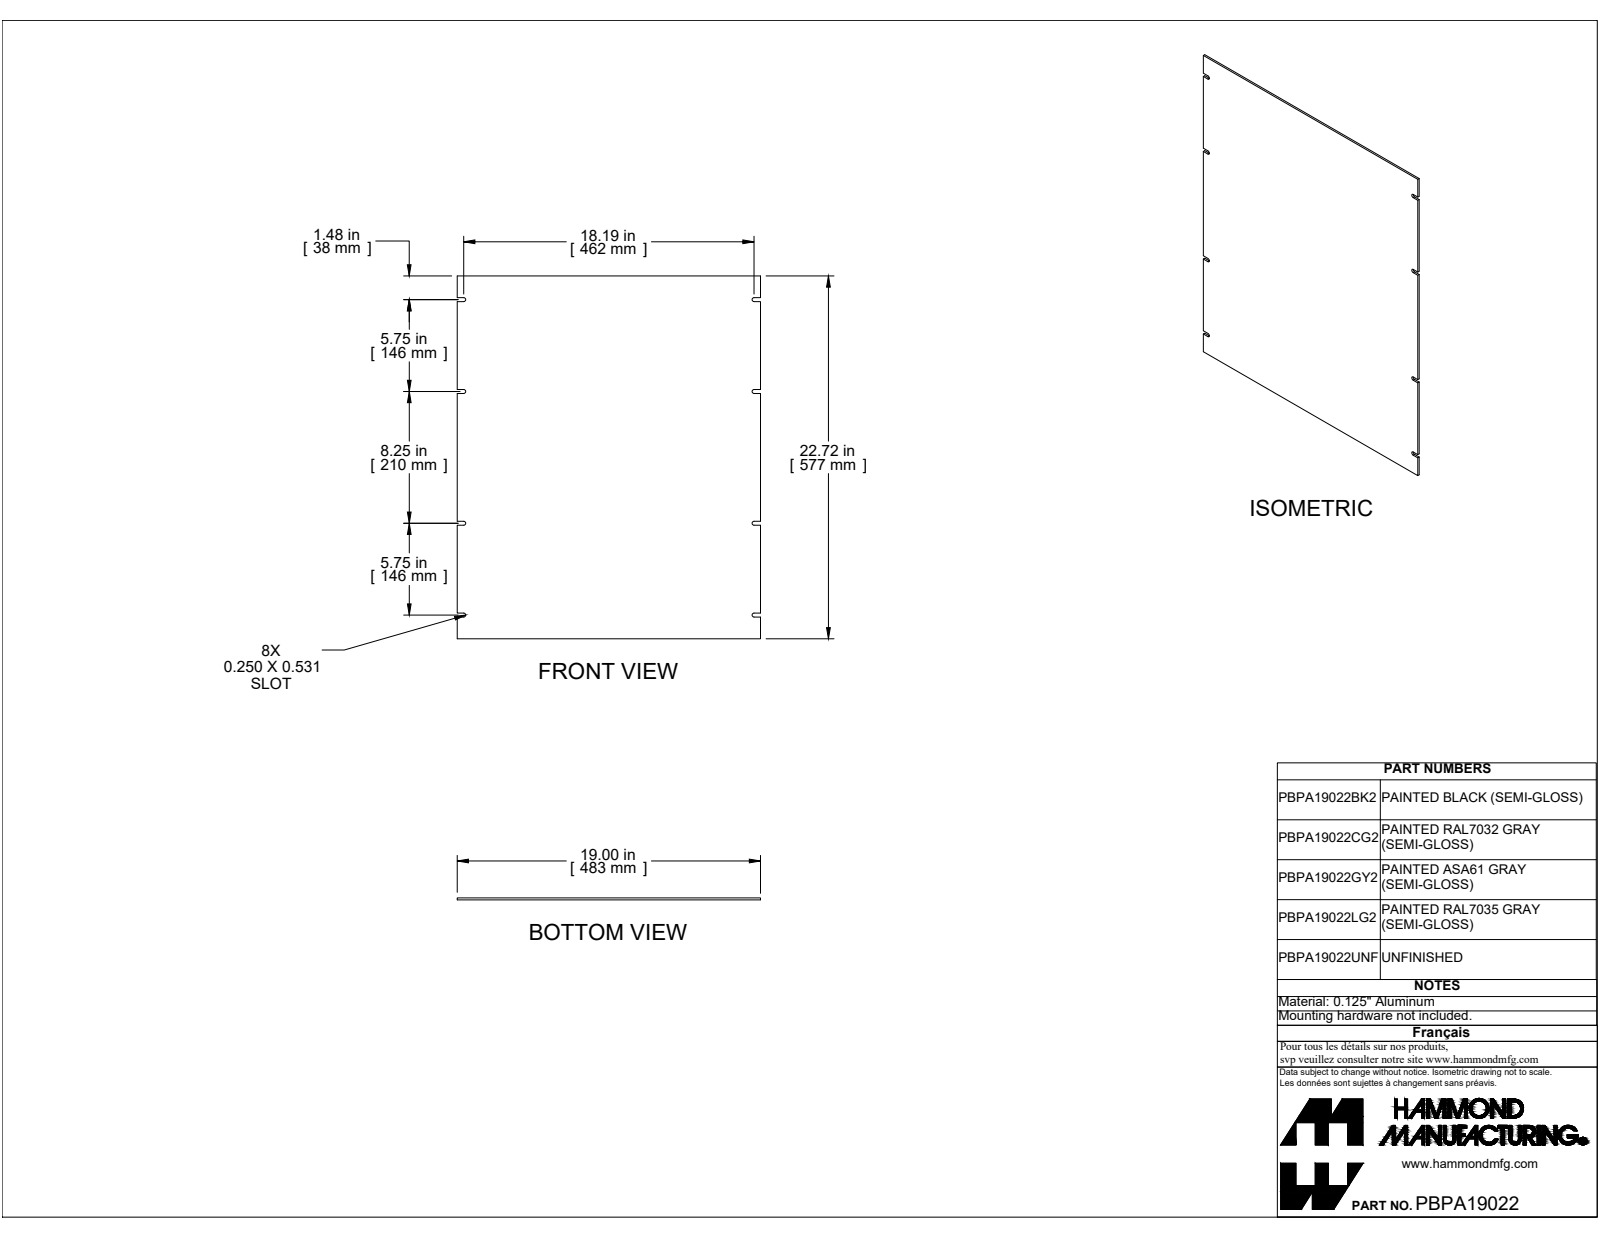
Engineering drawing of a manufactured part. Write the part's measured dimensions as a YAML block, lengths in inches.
part_name: "PBPA19022GY2"
step_written_by: "SolidWorks 2019 (CONFIG_CONTROL_DESIGN)"
units: inches
bodies: {solids: 1, faces: 38, planar: 30, cylindrical: 8, other: 0}
overall_size: [22.718, 19, 0.125]
volume: 53.83
surface_area: 872.7
partial_cylinders:
  - {radius: 0.125, count: 8}
face_to_face_distances: [0.125, 19, 22.718, 5.75, 14, 0.25, 1.359, 1.609, 7.109, 7.359]
